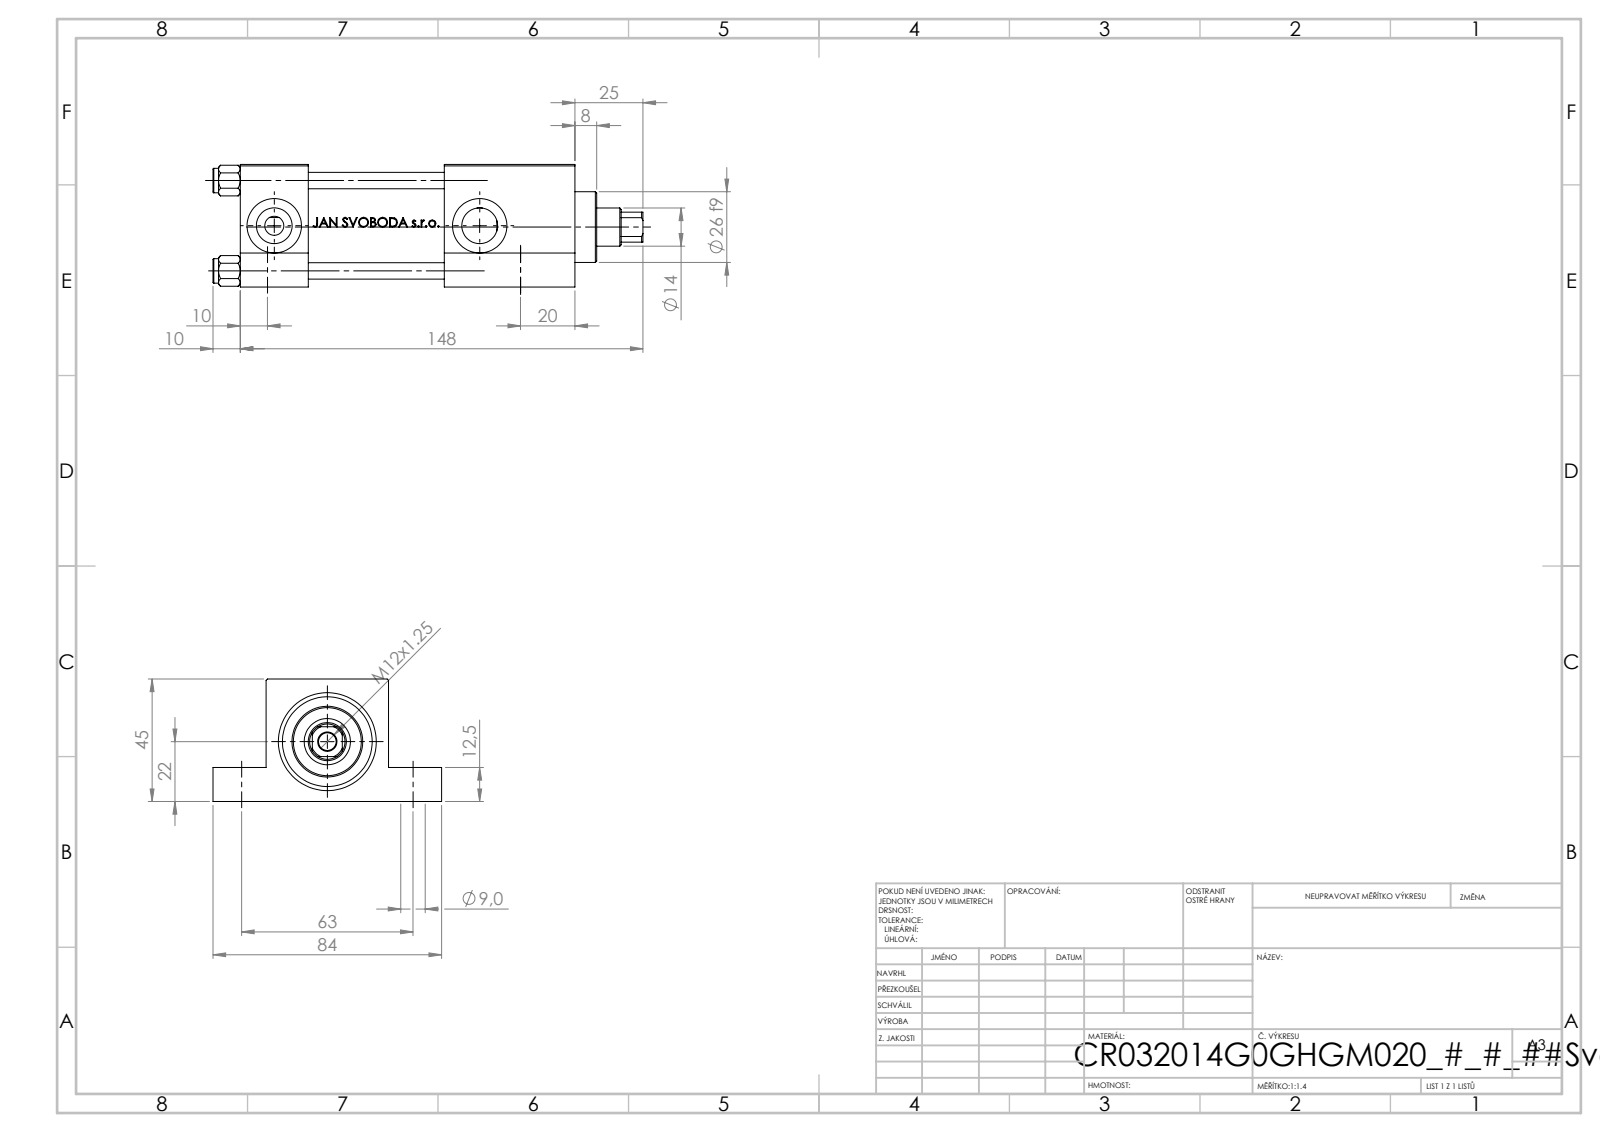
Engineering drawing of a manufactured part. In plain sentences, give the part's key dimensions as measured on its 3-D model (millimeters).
The part is named "V215CR_VCP_G; V215CR_G_TYCINKA; V215CR_G_Body; NUT_M5_G (+1 more)". Its 3-D file was written by "SolidWorks 2019 (CONFIG_CONTROL_DESIGN)". It is 11 solids with 1086 faces: 430 planar, 124 cylindrical and 532 other. Overall it measures 158 by 84 by 45 millimeters. Its volume is 227 965 cubic millimeters and its surface area 74 458 square millimeters. Round holes: 4 of diameter 6, 4 of diameter 9, 2 of diameter 7, 2 of diameter 13.16, 2 of diameter 20, 1 of diameter 6.5, 1 of diameter 14, 1 of diameter 17, 1 of diameter 24, 1 of diameter 32, 1 of diameter 33. Round bosses or shafts: 4 of diameter 9, 1 of diameter 38, 1 of diameter 26. Partial cylindrical surfaces (rounded edges, fillets, slot ends): 1 of radius 6.5. The main face-to-face distances are 45, 25, 12.5, 32.5, 98, 123, 19.5, 64.5, 50, 75. The hole center spacings are 33.2, 23.13, 23.83, 46.95, 63, 93, 112.33, 75.5.
